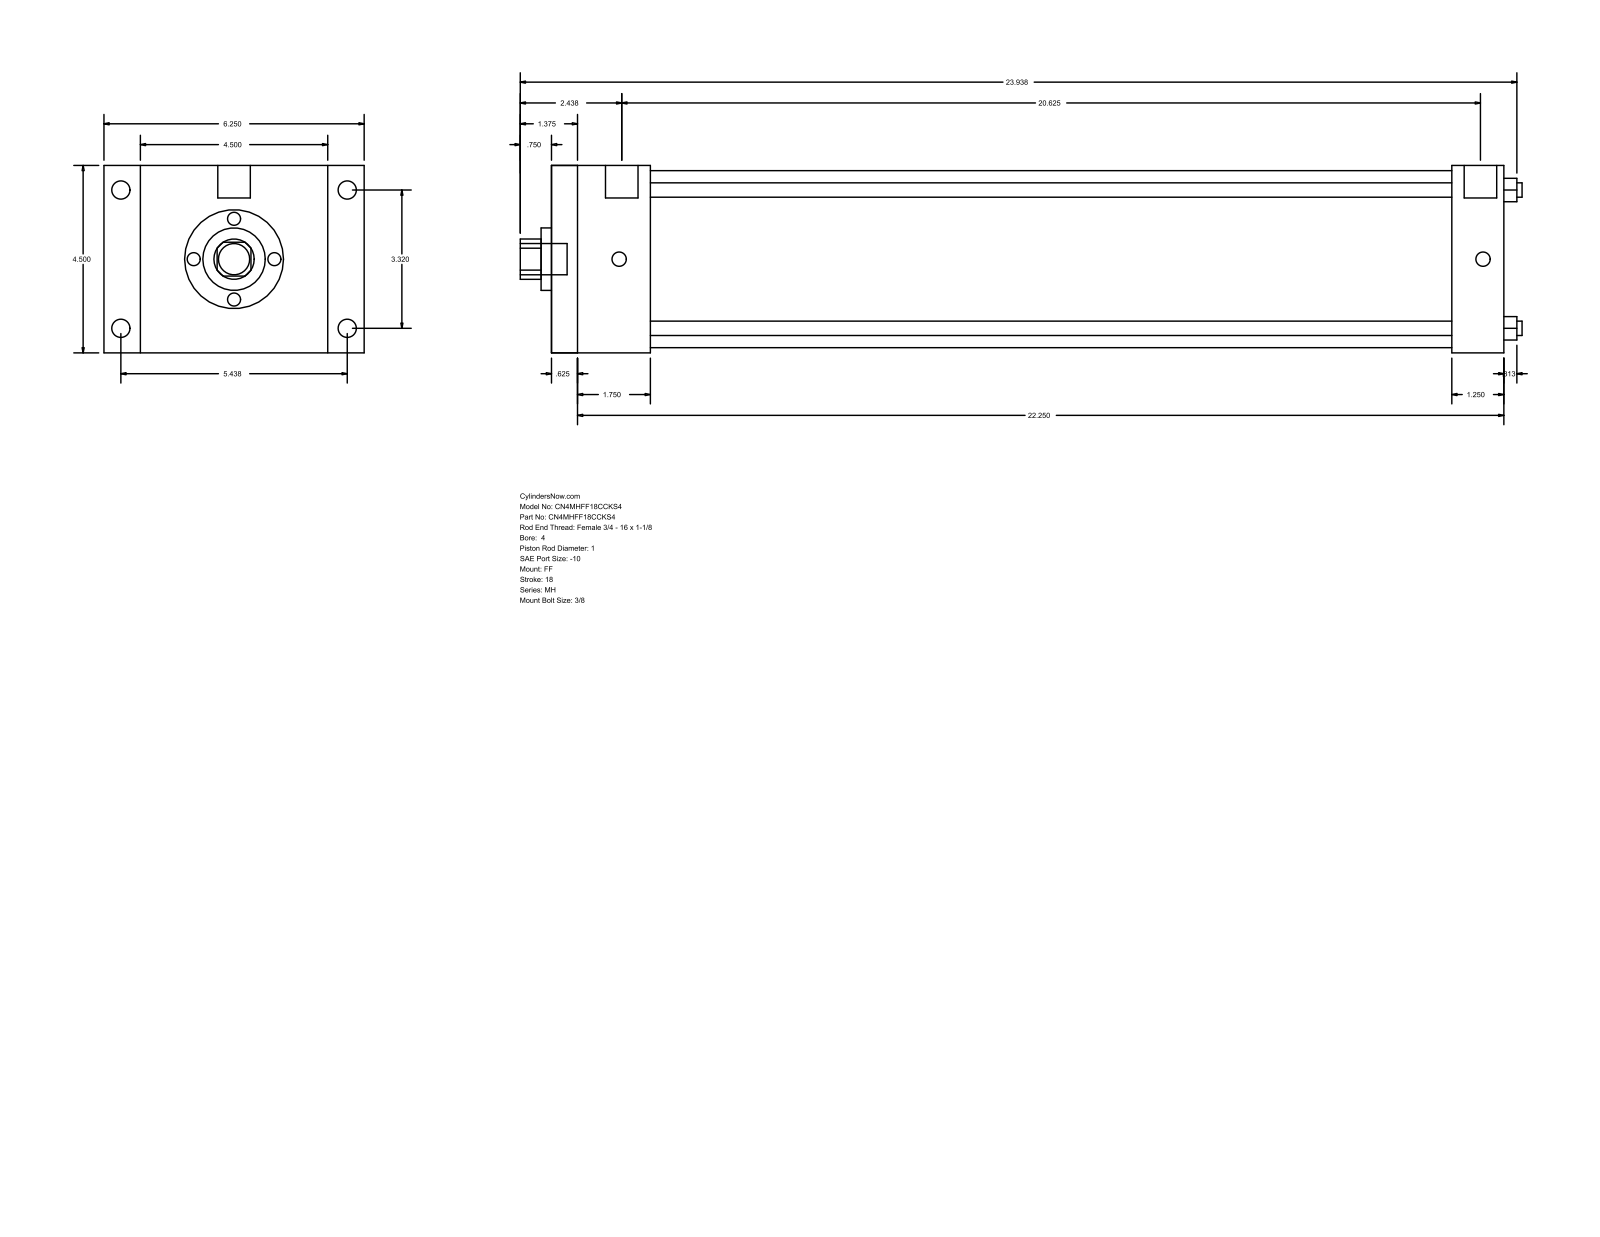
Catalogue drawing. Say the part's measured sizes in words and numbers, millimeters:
The part is named "MH_FF__0400_1". Its 3-D file was written by "GSSL Pune (CONFIG_CONTROL_DESIGN)". It is 0 solids with 92 faces: 64 planar, 28 cylindrical and 0 other. Overall it measures 611.19 by 158.75 by 114.3 millimeters. Round holes: 4 of diameter 8.76, 1 of diameter 25.4, 1 of diameter 38.1, 1 of diameter 107.95. Round bosses or shafts: 4 of diameter 11.13, 4 of diameter 8.73, 2 of diameter 19.84, 1 of diameter 19.05. Partial cylindrical surfaces (rounded edges, fillets, slot ends): 1 of radius 12.29. The main face-to-face distances are 114.3, 581.03, 15.87, 565.16, 60.33, 44.46, 520.7, 549.28, 533.41, 488.95. The hole center spacings are 59.62, 84.32, 119.25.
